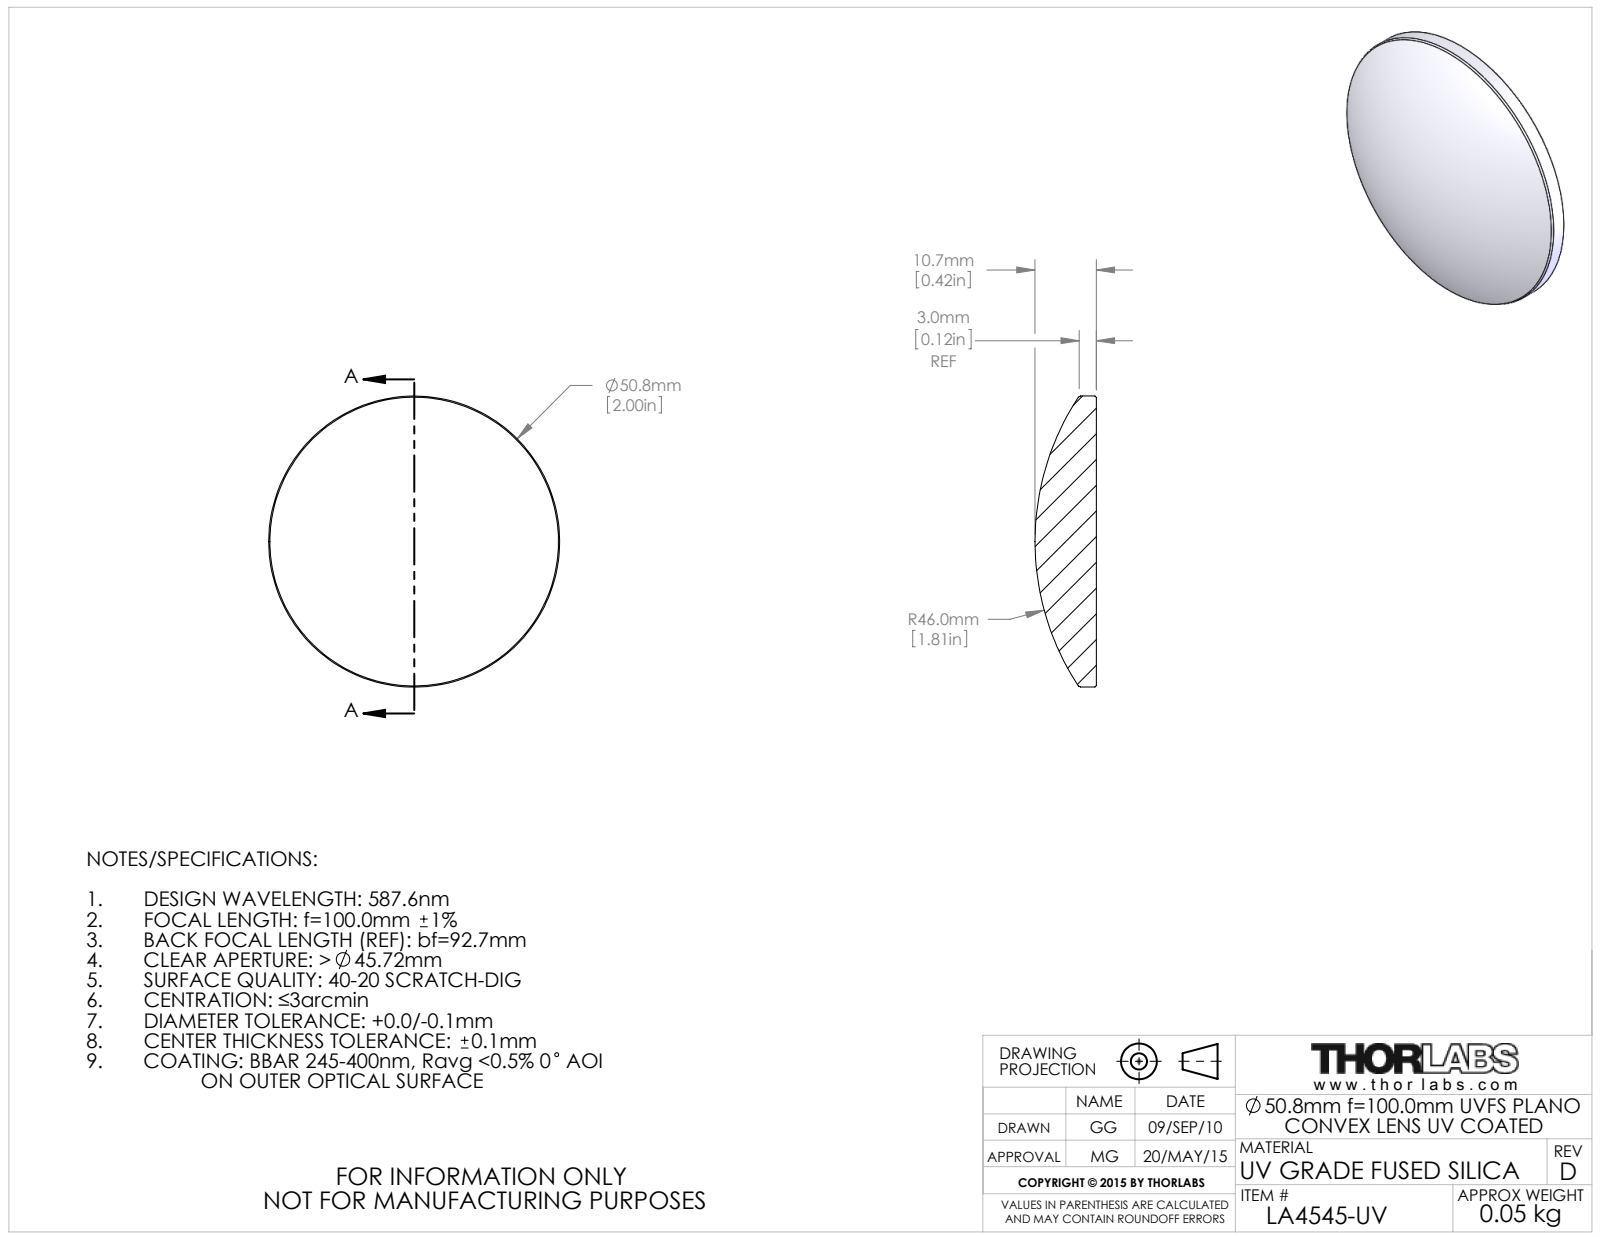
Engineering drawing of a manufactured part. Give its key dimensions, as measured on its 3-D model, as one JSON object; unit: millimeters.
{"part_name": "4294-E0W", "step_written_by": "SolidWorks 2014 (CONFIG_CONTROL_DESIGN)", "units": "millimeters", "bodies": {"solids": 1, "faces": 9, "planar": 1, "cylindrical": 2, "other": 6}, "overall_size": [50.8, 50.8, 10.7], "volume_mm3": 14097, "surface_area_mm2": 4685, "round_bosses_or_shafts": [[50.8, 1]]}
